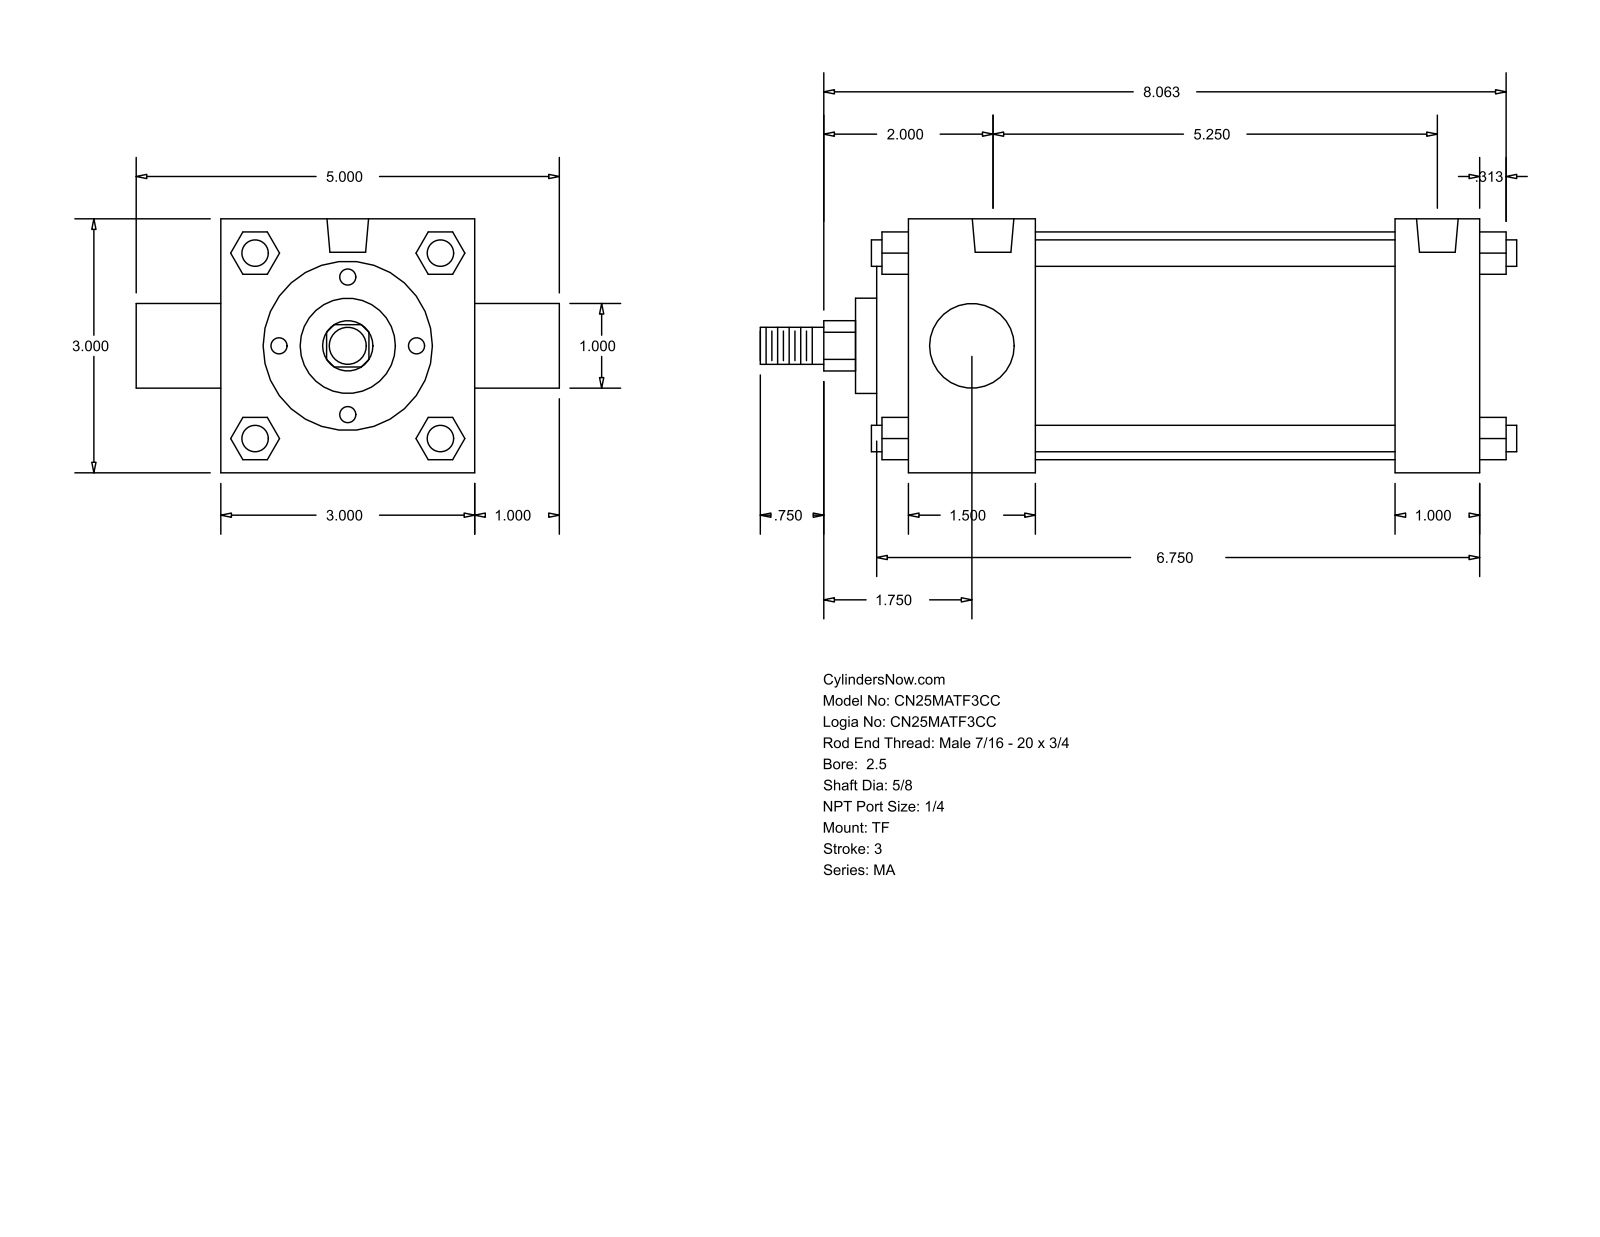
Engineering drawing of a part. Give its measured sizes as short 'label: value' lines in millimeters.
name: MA_TF__0250_0.625
written by: GSSL Pune (CONFIG_CONTROL_DESIGN)
unit: mm
bodies: 0 solids, 122 faces (93 planar, 29 cylindrical, 0 other)
size: 227.01 × 127 × 76.2
holes: 3× ⌀7.94, 2× ⌀12.49
bosses: 4× ⌀7.94, 1× ⌀68.33, 1× ⌀50.8, 1× ⌀28.57, 1× ⌀25.4, 1× ⌀15.88, 1× ⌀11.11
rounds: 1× R7.54
face distances: 76.2, 171.45, 25.4, 38.1, 146.05, 107.95, 133.35, 12.7, 9.52, 47.62
hole spacings: 133.35
